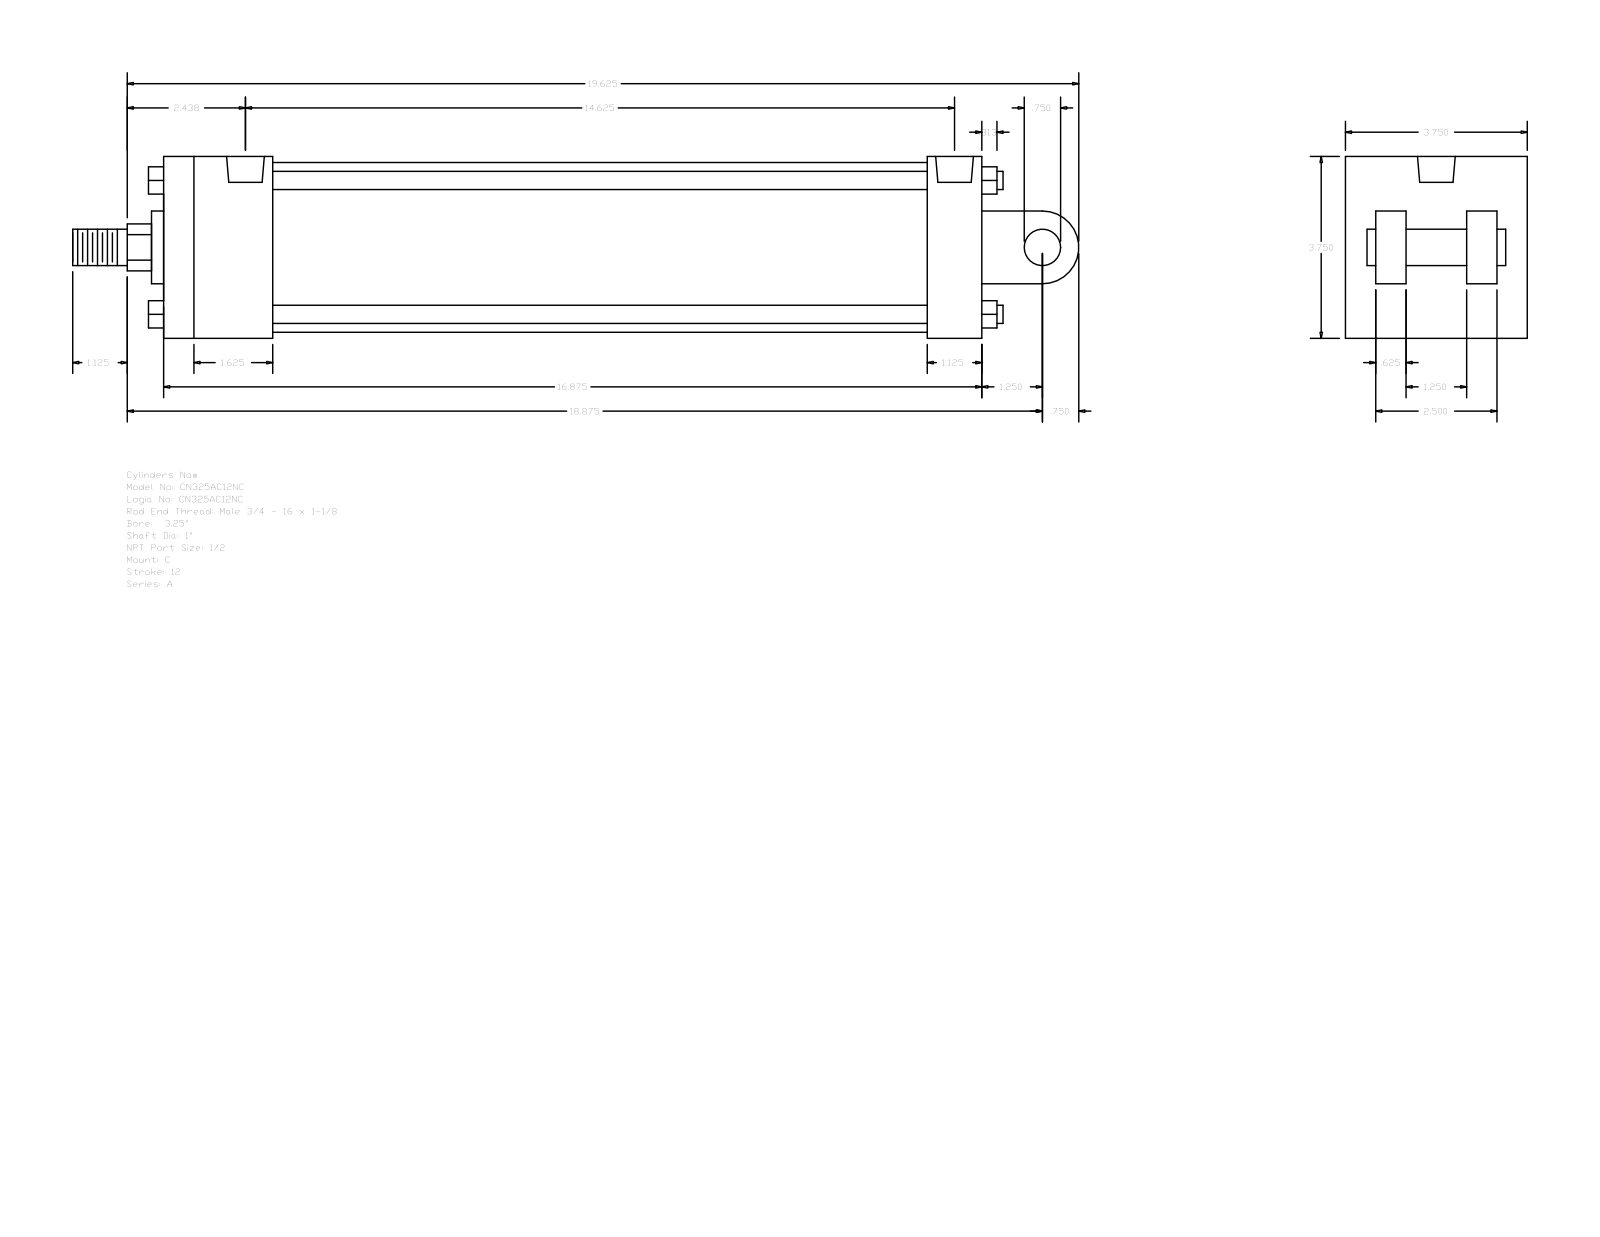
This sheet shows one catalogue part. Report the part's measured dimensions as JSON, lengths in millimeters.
{"part_name": "A_C__0325_1", "step_written_by": "GSSL Pune (CONFIG_CONTROL_DESIGN)", "units": "millimeters", "bodies": {"solids": 0, "faces": 135, "planar": 102, "cylindrical": 33, "other": 0}, "overall_size": [527.05, 95.25, 95.25], "round_holes": [[8.73, 4], [19.77, 2]], "round_bosses_or_shafts": [[9.53, 4], [19.05, 2], [88.9, 1], [38.1, 1], [25.4, 1]], "partial_cylinders_radius": [[12.29, 1], [19.05, 1]], "face_to_face_distances": [95.24, 428.63, 15.87, 63.5, 79.37, 31.74, 47.63, 66.67, 400.05, 28.58], "hole_center_spacings": [3.18, 365.12, 368.3, 371.48]}
